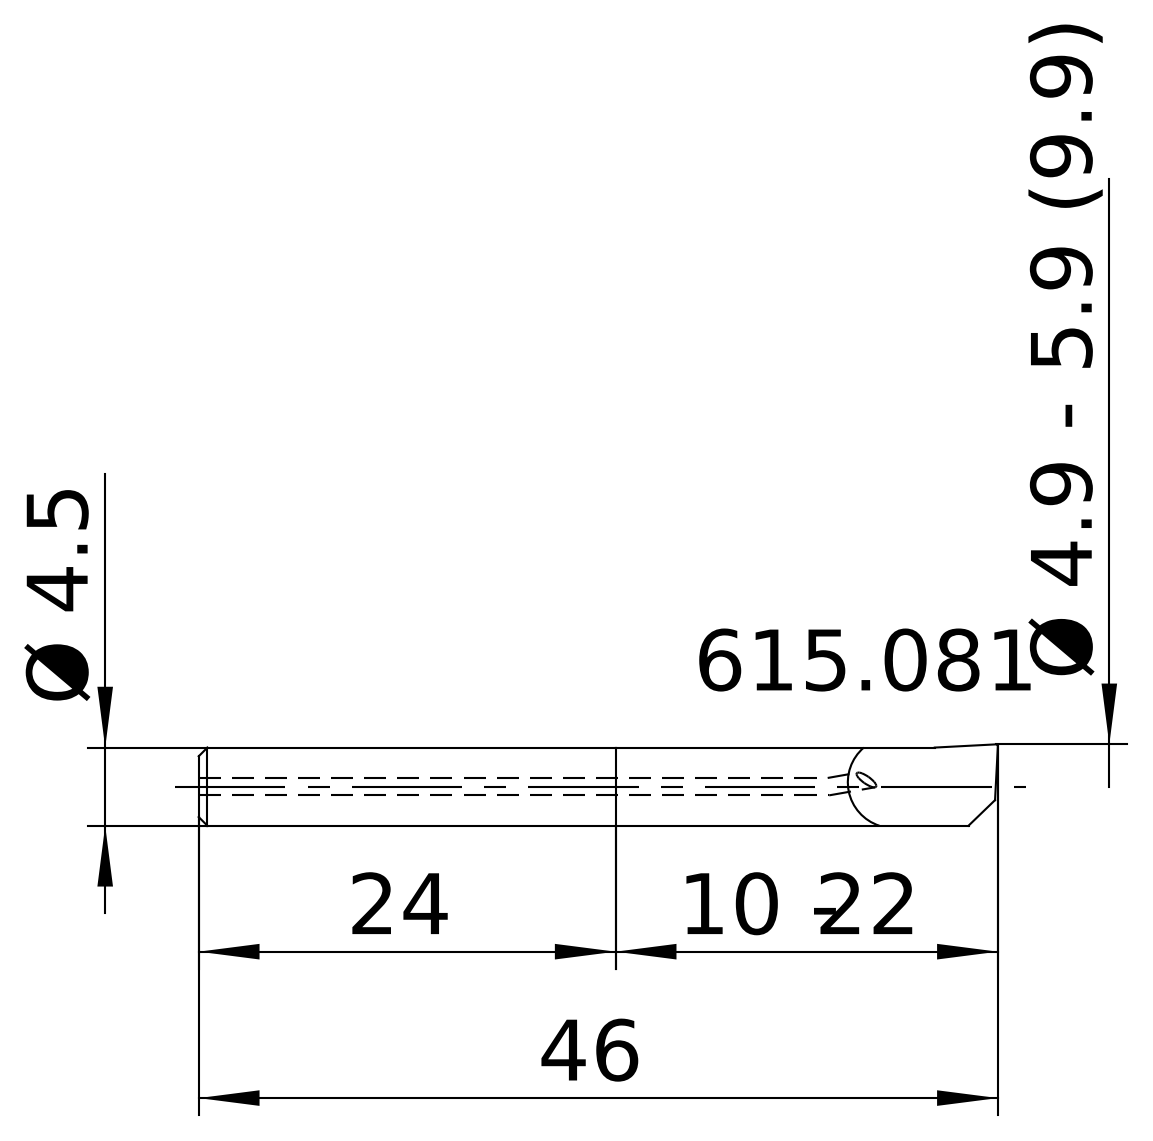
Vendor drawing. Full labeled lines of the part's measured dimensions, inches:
Part name (STEP PRODUCT): Fase2
STEP written by: ACIS (automotive_design)
Units: inches
Bodies: 1 solid, 19 faces (11 planar, 5 cylindrical, 3 other)
Overall size (bounding box): 1.811 × 0.185 × 0.177
Volume: 0.041 in³ · Surface area: 1.24 in²
Round holes (diameter × count): ⌀0.039 ×1
Round bosses / shafts (diameter × count): ⌀0.177 ×1
Partial cylindrical surfaces — rounded edges, fillets, slot ends (radius × count): R0.01 ×1
Main face-to-face distances: 1.811
